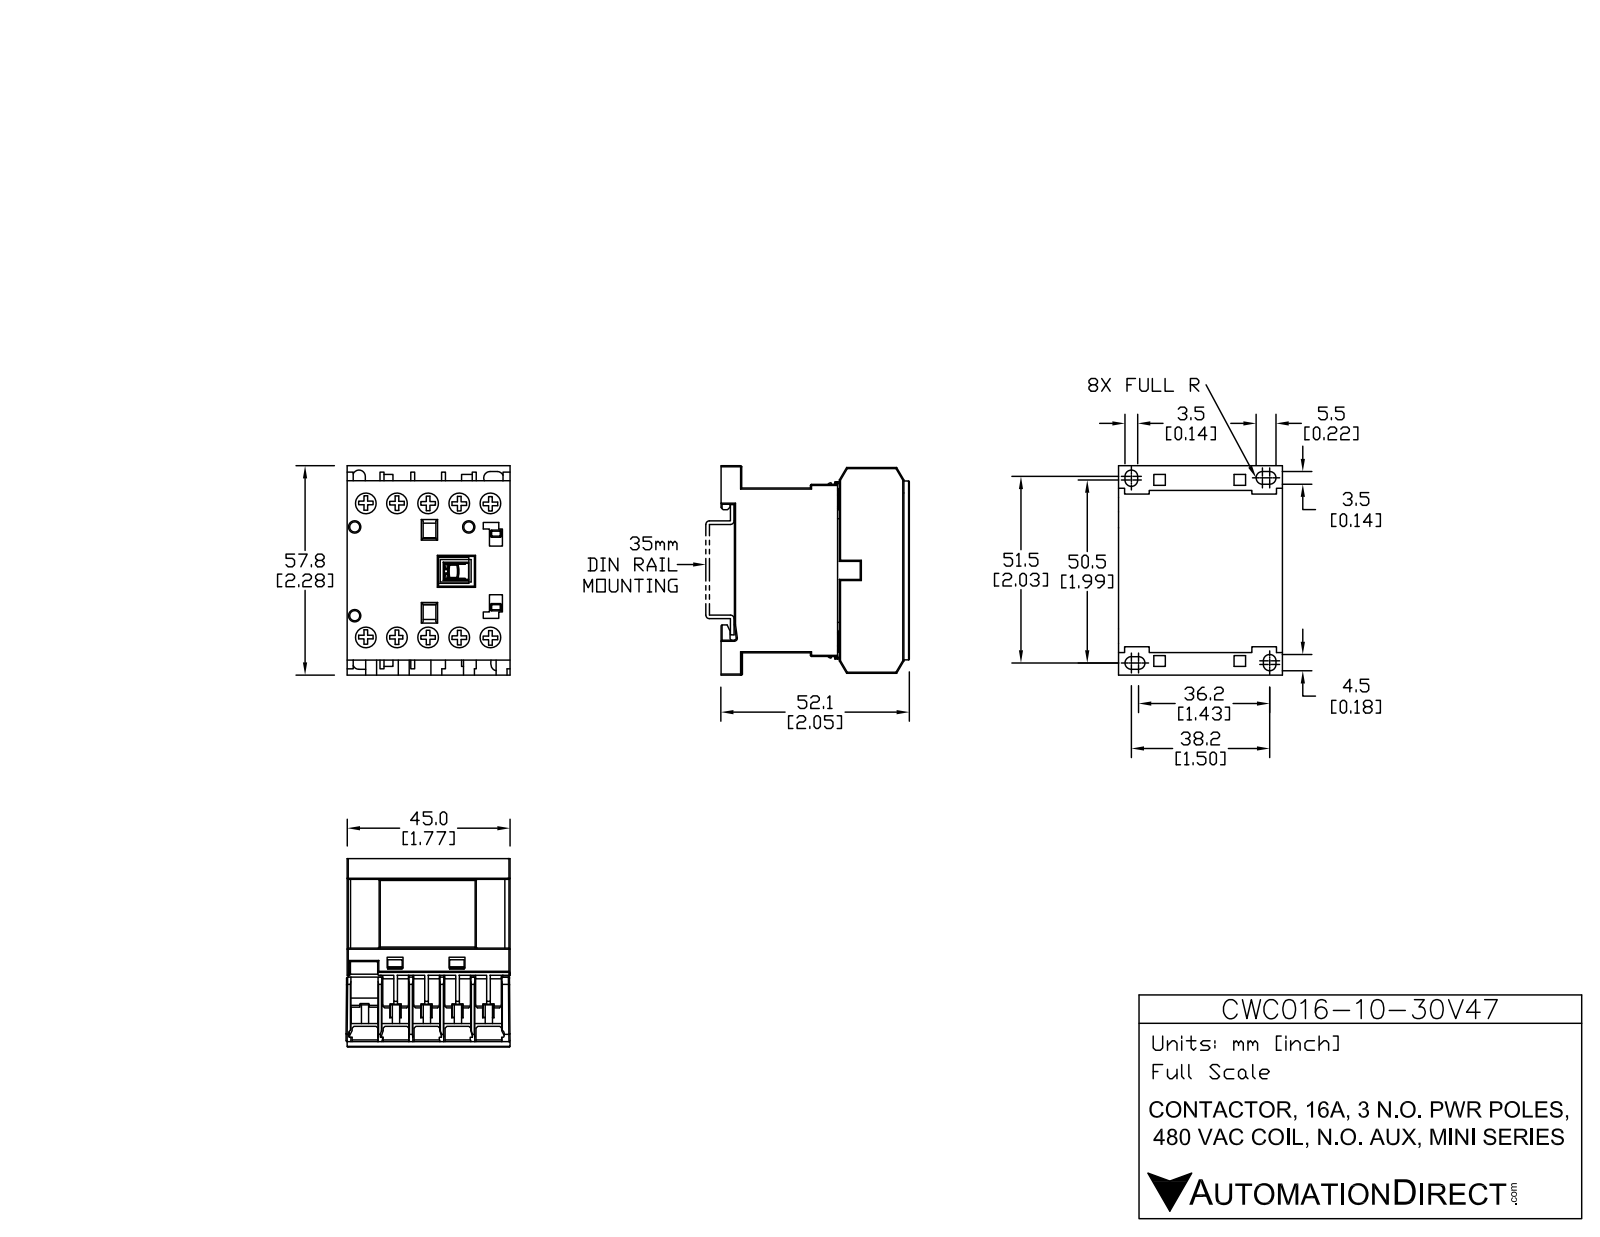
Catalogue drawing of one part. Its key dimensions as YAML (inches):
part_name: "CWC16-10-30V47"
step_written_by: "SolidWorks 2013 (AUTOMOTIVE_DESIGN)"
units: inches
bodies: {solids: 15, faces: 535, planar: 445, cylindrical: 90, other: 0}
overall_size: [2.285, 2.052, 1.801]
volume: 5.927
surface_area: 47.18
round_holes:
  - {diameter: 0.244, count: 10}
  - {diameter: 0.11, count: 3}
round_bosses_or_shafts:
  - {diameter: 0.232, count: 10}
partial_cylinders:
  - {radius: 0.012, count: 20}
  - {radius: 0.068, count: 6}
  - {radius: 0.068, count: 2}
  - {radius: 0.013, count: 1}
  - {radius: 0.017, count: 1}
  - {radius: 0.022, count: 1}
face_to_face_distances: [0.325, 1.791, 0.049, 0.65, 0.374, 0.217, 0.699, 0.202, 0.419, 0.276]
hole_center_spacings: [0.337, 1.494, 0.673, 1.603, 1.455, 1.01, 1.771, 0.272]
